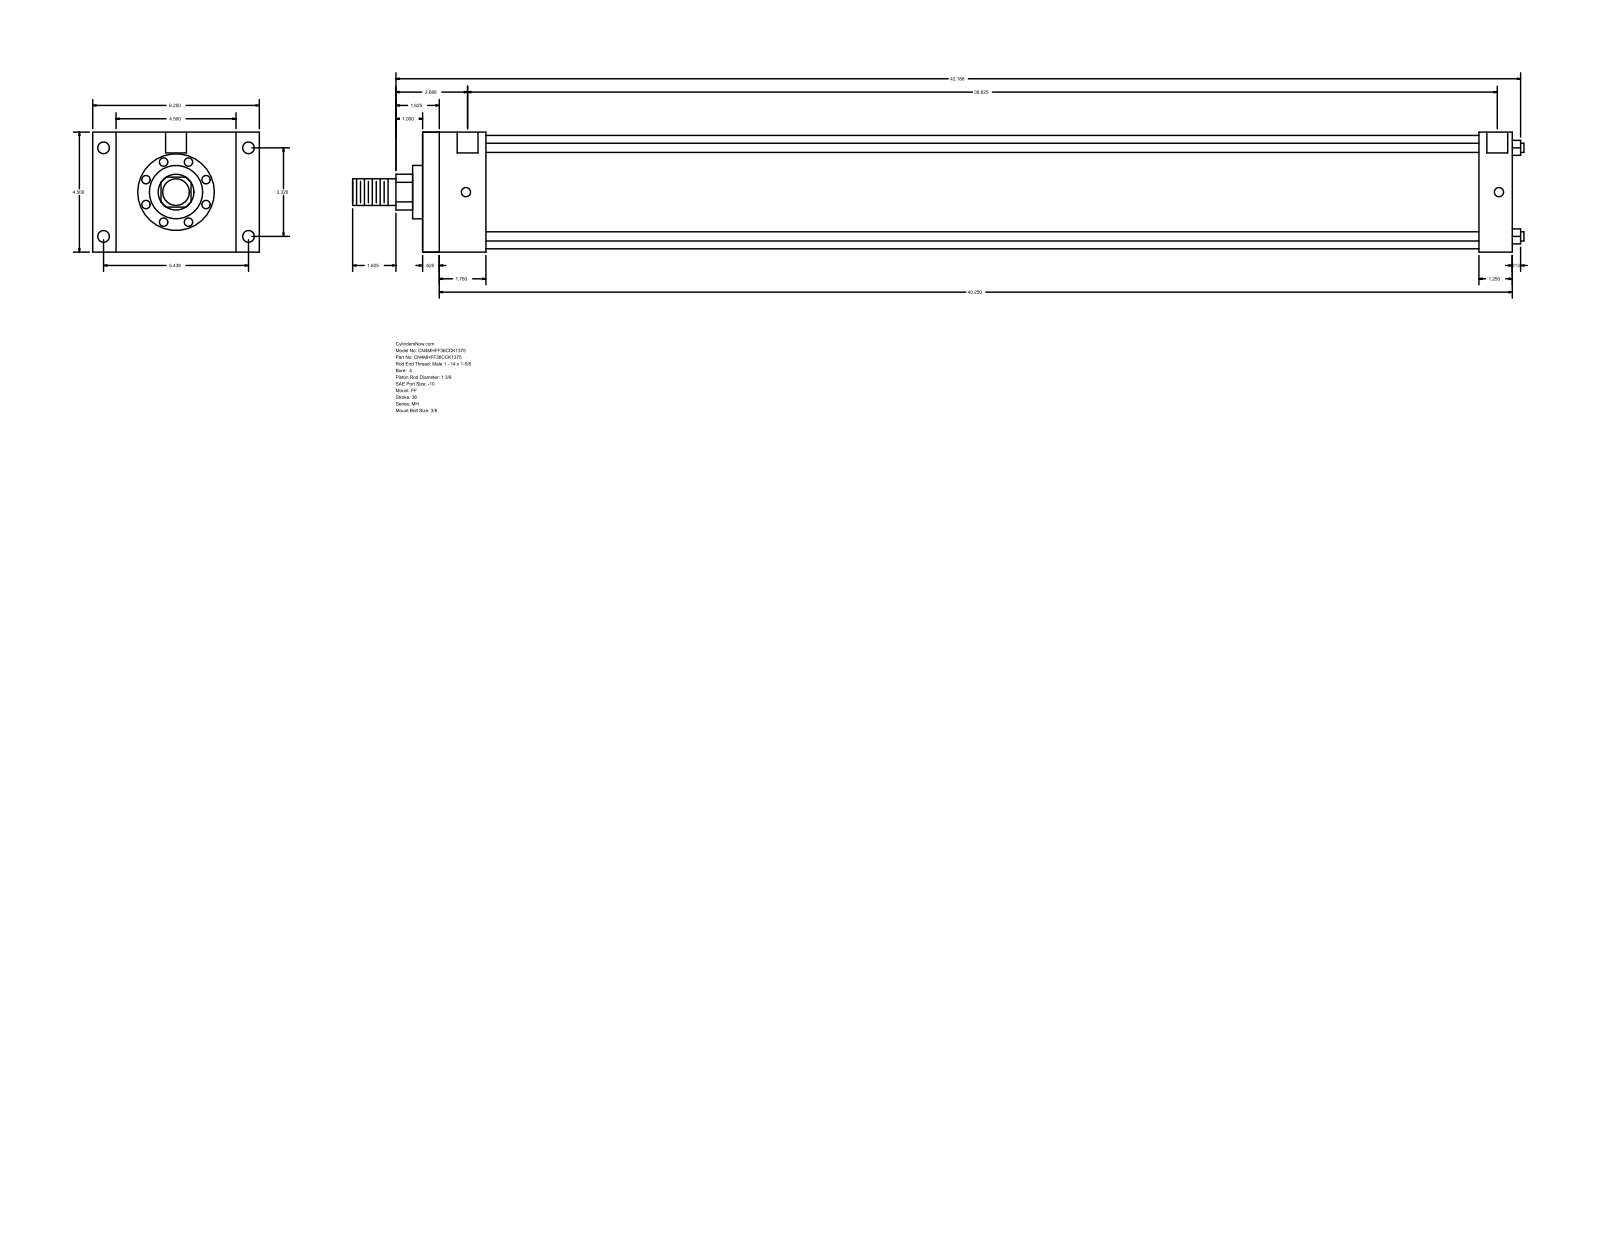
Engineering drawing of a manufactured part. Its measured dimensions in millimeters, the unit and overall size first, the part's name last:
Units: millimetres
Overall size (bounding box): 1116.01 × 158.75 × 114.3
Round holes (diameter × count): ⌀8.73 ×4, ⌀11.13 ×4, ⌀19.84 ×2
Round bosses / shafts (diameter × count): ⌀8.76 ×4, ⌀107.95 ×1, ⌀50.8 ×1, ⌀34.92 ×1, ⌀25.4 ×1
Partial cylindrical surfaces — rounded edges, fillets, slot ends (radius × count): R17.06 ×1
Main face-to-face distances: 114.3, 1038.22, 15.87, 1022.35, 60.32, 44.45, 977.9, 1006.48, 990.61, 946.16
Hole centre spacings: 84.32, 138.12, 161.82, 984.25, 1.58, 1.59, 981.08, 982.66
Bodies: 0 solids, 92 faces (64 planar, 28 cylindrical, 0 other)
Part name (STEP PRODUCT): MH_FF__0400_1.375
STEP written by: GSSL Pune (CONFIG_CONTROL_DESIGN)
